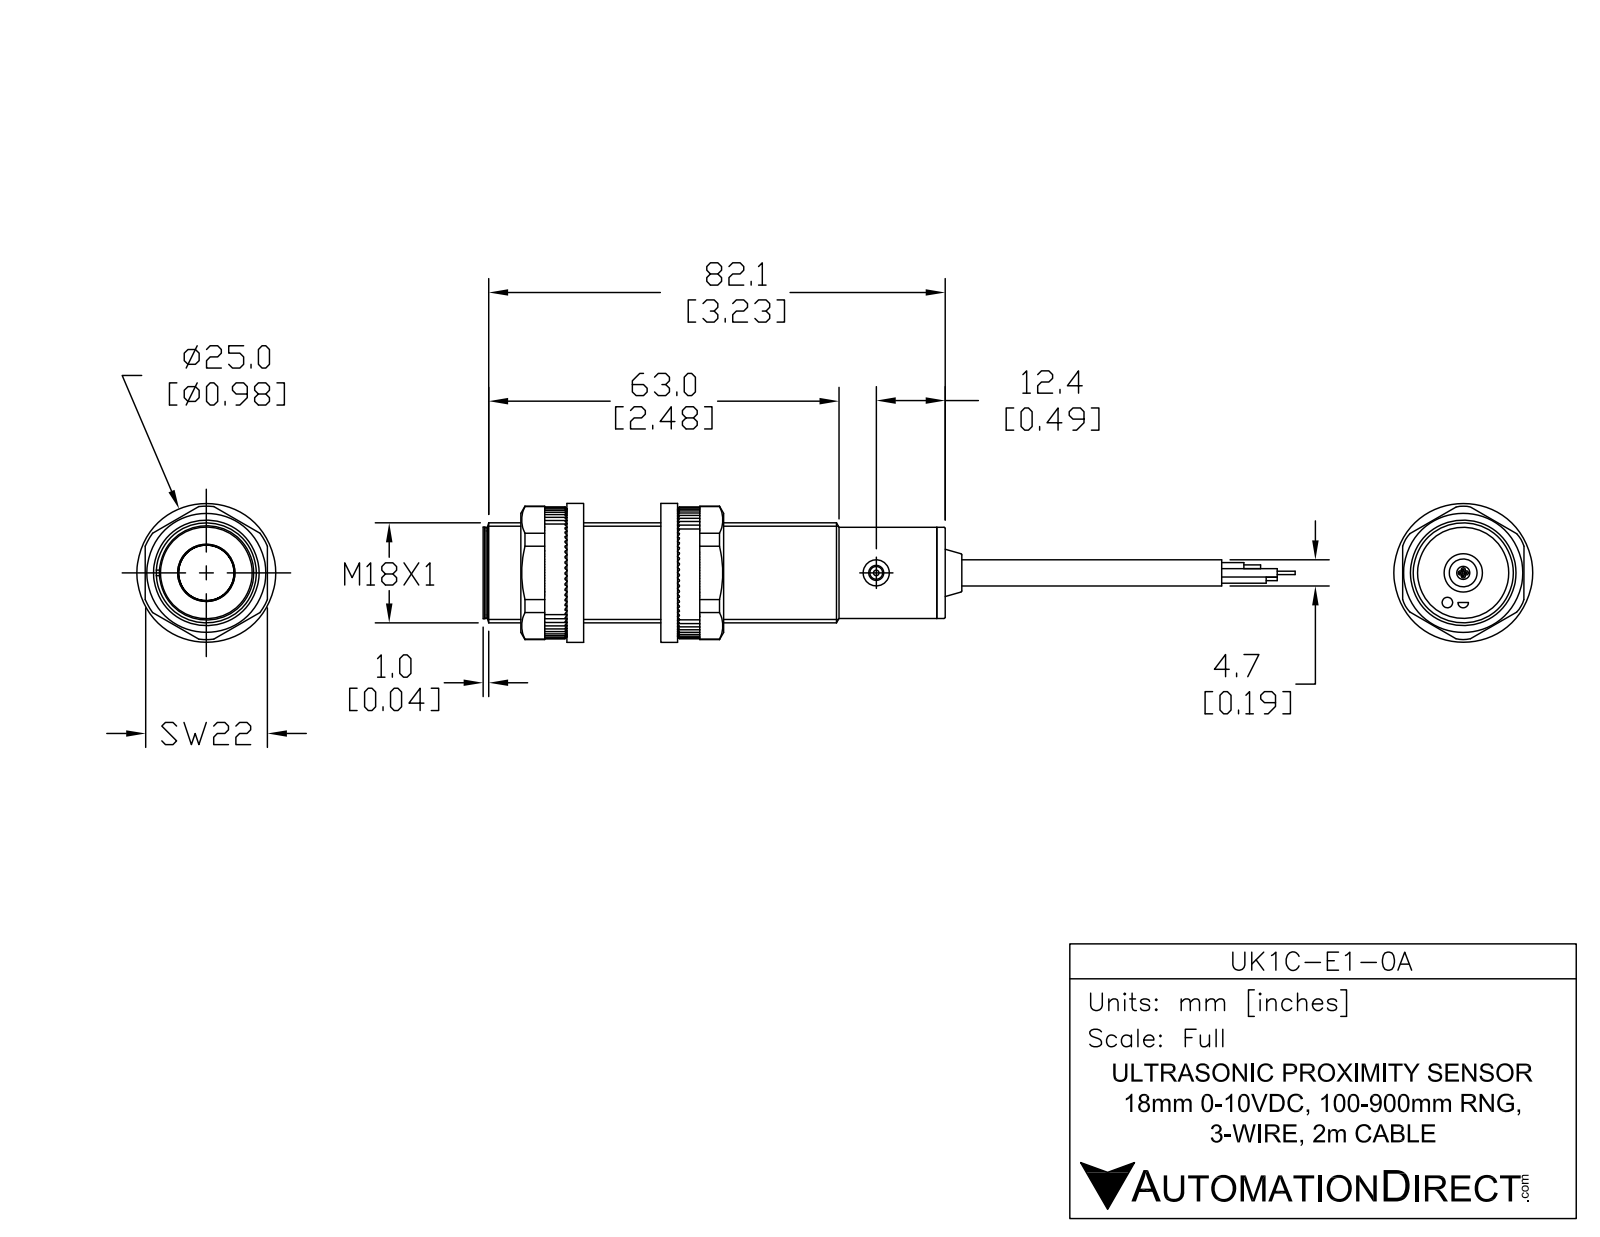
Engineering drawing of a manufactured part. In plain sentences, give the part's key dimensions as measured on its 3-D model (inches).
The part is named "UK1C-E1-0A". Its 3-D file was written by "SolidWorks 2017 (AUTOMOTIVE_DESIGN)". It is 6 solids with 55 faces: 17 planar, 24 cylindrical and 14 other. Overall it measures 4.832 by 0.709 by 0.709 inches. Its volume is 1.285 cubic inches and its surface area 10.69 square inches. Round holes: 2 of diameter 0.185, 1 of diameter 0.106. Round bosses or shafts: 1 of diameter 0.709, 1 of diameter 0.646, 1 of diameter 0.622, 1 of diameter 0.374, 1 of diameter 0.189, 1 of diameter 0.091. The main face-to-face distances are 3.193, 3.252, 0.059, 0.039, 3.232, 3.291, 0.041, 3.234, 3.293, 3.257.
